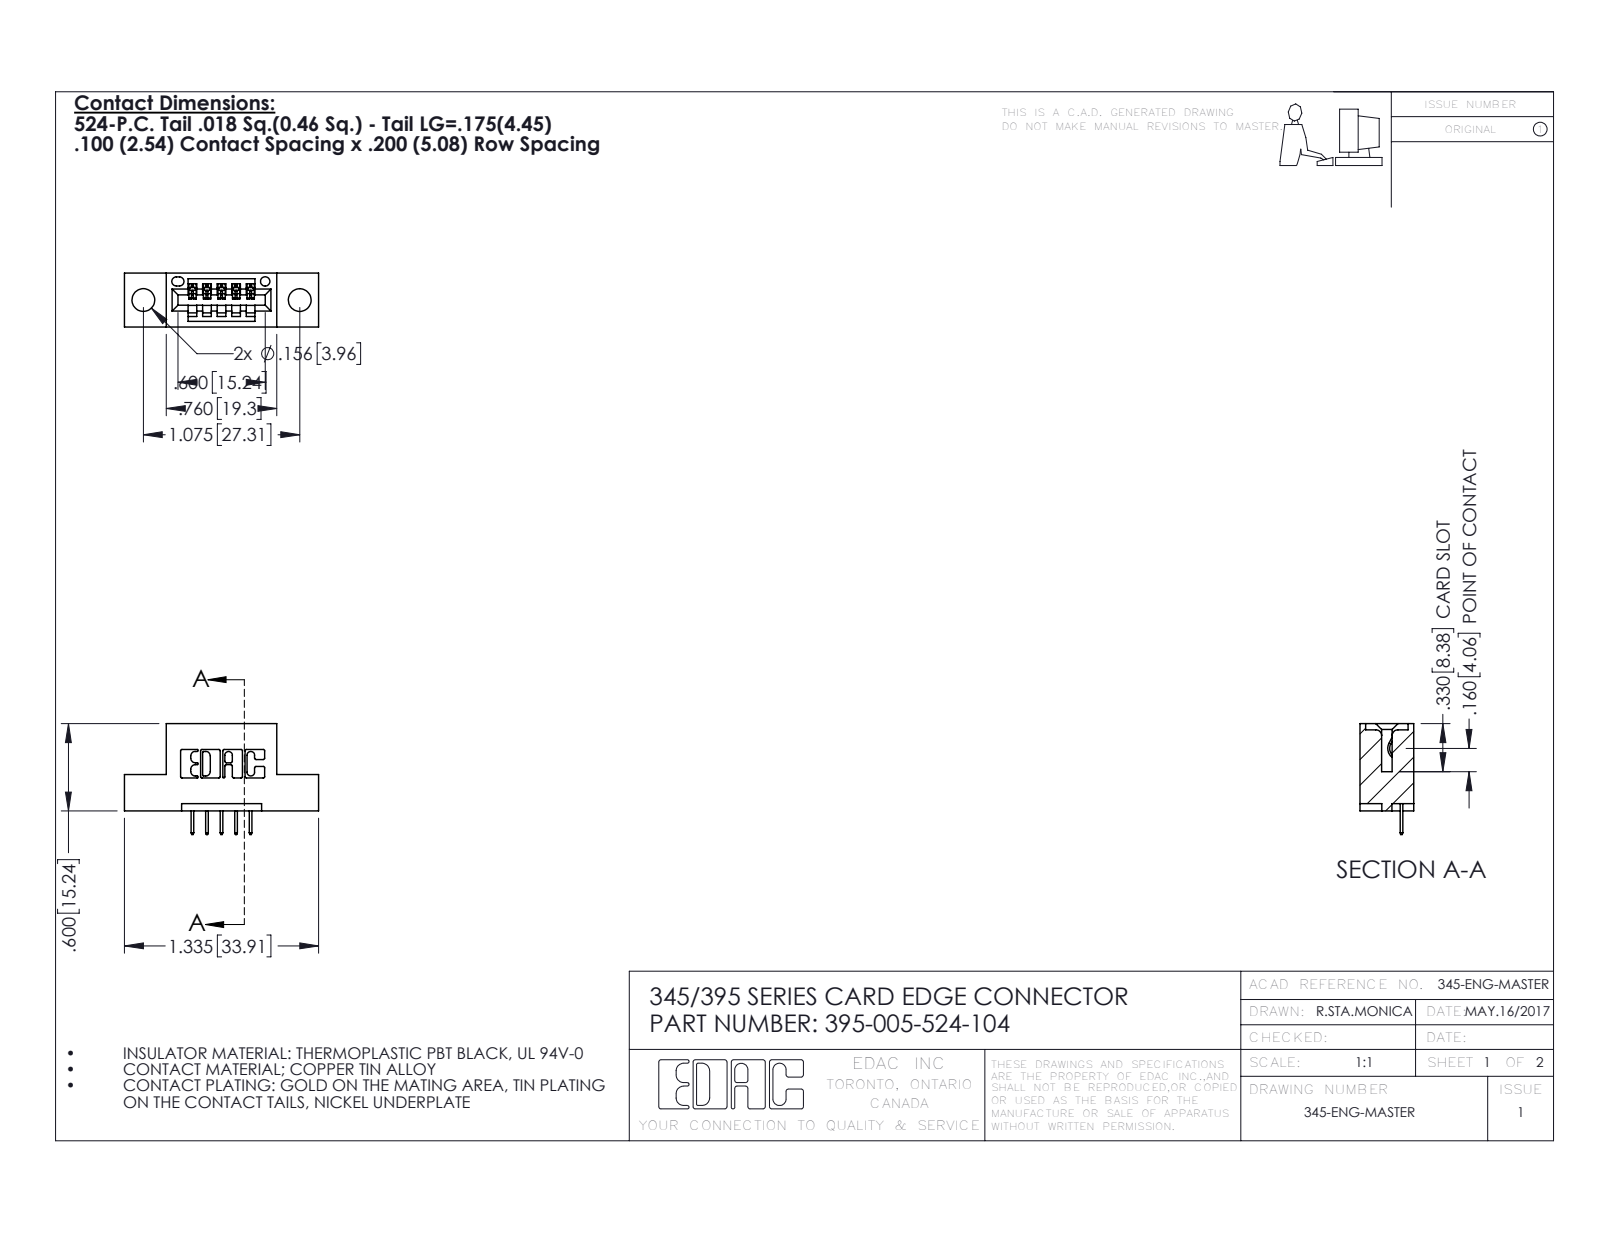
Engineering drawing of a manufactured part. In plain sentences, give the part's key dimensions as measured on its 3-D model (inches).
The part is named "345 Part_Flush Mounting Lugs - 0.156 Dia-TH; 395-005-524-104; 345-292-001_345-293-124". Its 3-D file was written by "SolidWorks 2016 (CONFIG_CONTROL_DESIGN)". It is 6 solids with 436 faces: 310 planar, 126 cylindrical and 0 other. Overall it measures 1.335 by 0.762 by 0.37 inches. Its volume is 0.171 cubic inches and its surface area 4.614 square inches. Round holes: 2 of diameter 0.156, 1 of diameter 0.064. Partial cylindrical surfaces (rounded edges, fillets, slot ends): 22 of radius 0.01, 10 of radius 0.006, 6 of radius 0.007, 6 of radius 0.031, 3 of radius 0.026, 2 of radius 0.031, 2 of radius 0.04, 1 of radius 0.014. The main face-to-face distances are 0.2, 0.37, 0.1, 0.298, 0.072, 0.25, 0.06, 0.025, 0.55, 0.35. The hole center spacings are 0.27, 0.847, 1.075.
